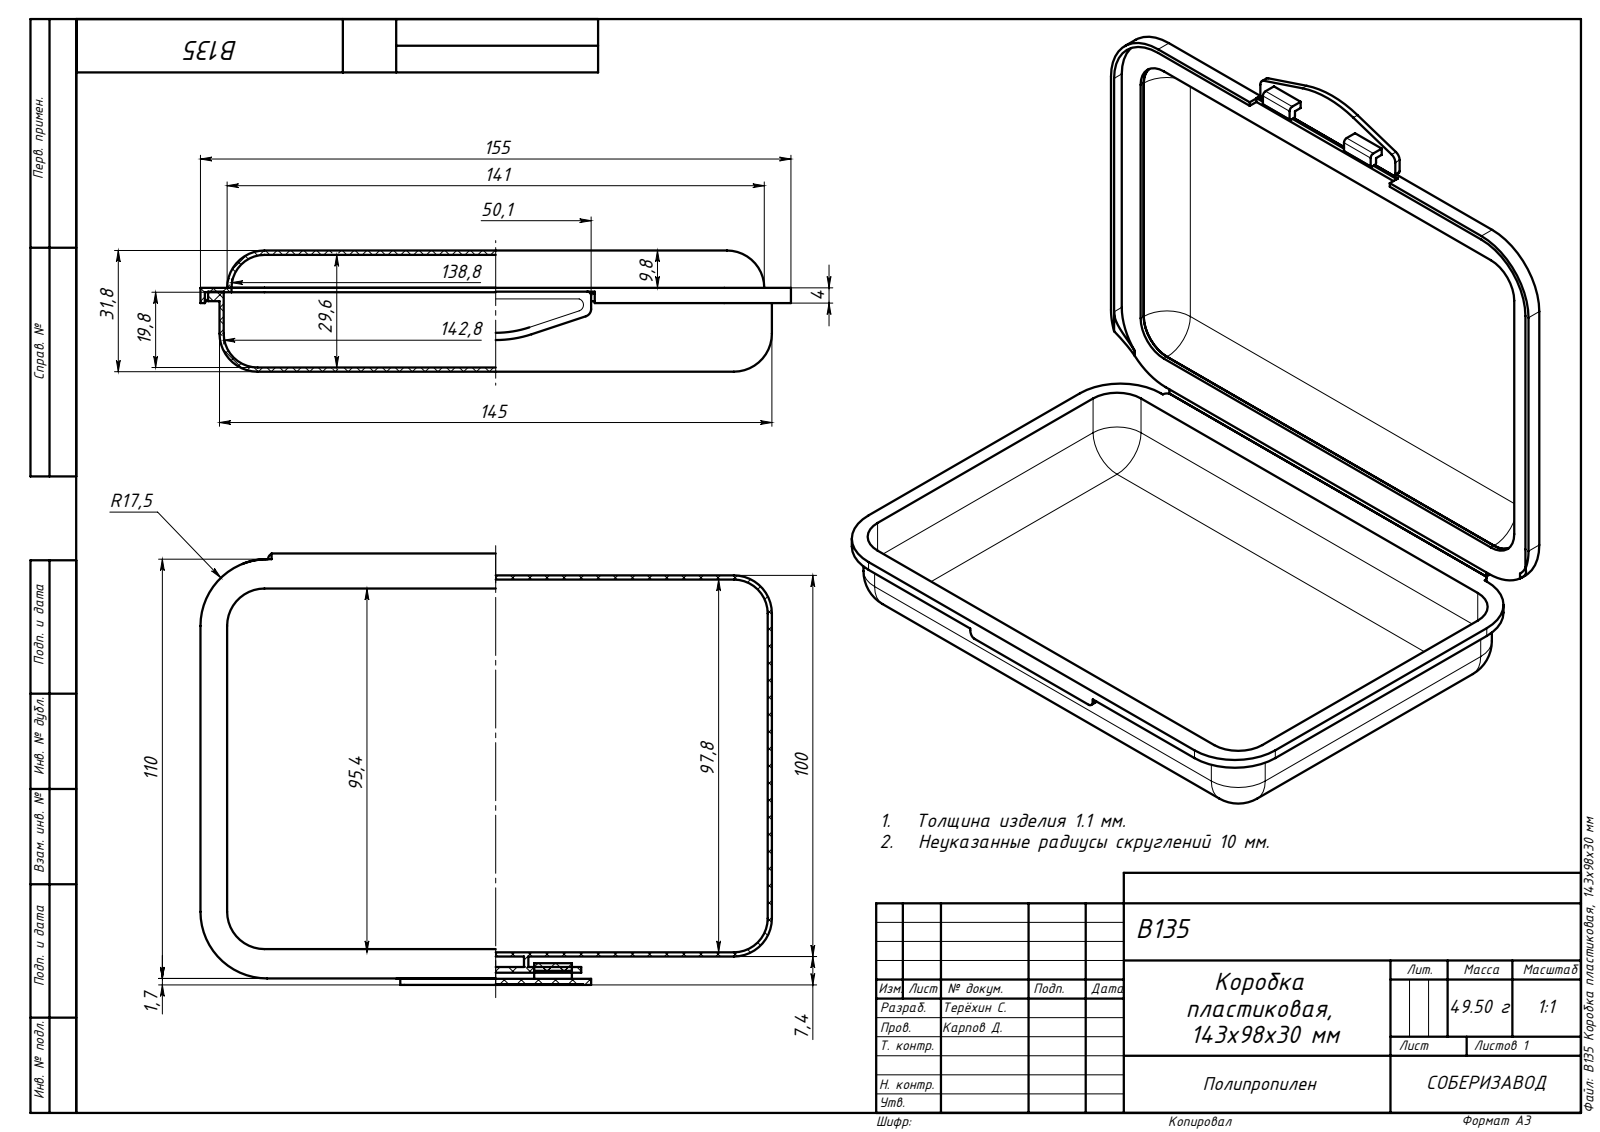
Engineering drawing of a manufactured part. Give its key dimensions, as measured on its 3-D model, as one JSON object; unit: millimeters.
{"part_name": "B135 Защёлка_00; B135 Крышка_00; B135 Коробка пластиковая, 143x98x30 мм; B135 Емкость_00", "step_written_by": "SolidWorks 2019 (AUTOMOTIVE_DESIGN)", "units": "millimeters", "bodies": {"solids": 4, "faces": 160, "planar": 83, "cylindrical": 59, "other": 18}, "overall_size": [155, 114.6, 31.8], "volume_mm3": 53265, "surface_area_mm2": 92387, "partial_cylinders_radius": [[8.65, 8], [8.9, 8], [10, 8], [9.8, 4], [15, 4], [16.35, 4], [17.5, 4], [1, 3]], "face_to_face_distances": [1.15, 1.1, 31.8, 30.7, 30.65, 29.55, 9.8, 8.65, 22, 20.9]}
